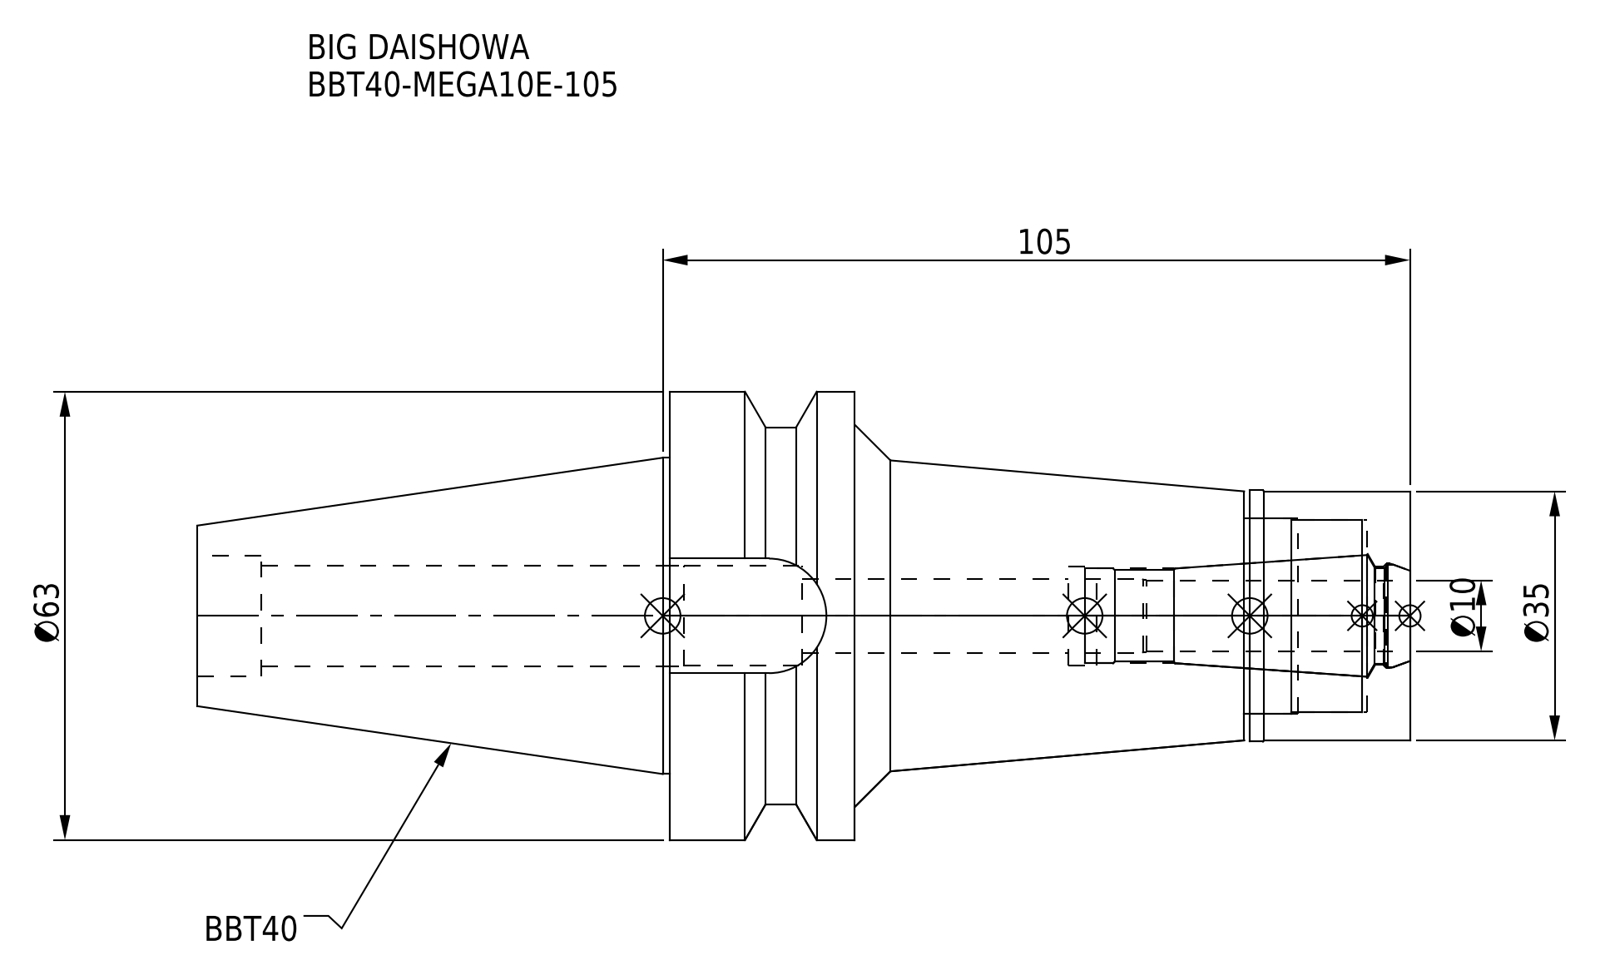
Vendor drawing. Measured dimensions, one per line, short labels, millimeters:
name: DXF_TEMP_ASSY_ASM_4_ASM.stp; BBT40ME10105-100_ASM.stp; MEN10_1.stp; BBT40-MEGA10E-105_1.stp (+3 more)
written by: SolidWorks 2019 (CONFIG_CONTROL_DESIGN)
unit: mm
bodies: 2 solids, 81 faces (21 planar, 40 cylindrical, 20 other)
size: 170.4 × 63 × 63
volume: 202 293 mm³; area: 38 719 mm²
holes: 1× ⌀10.4, 1× ⌀13.3, 1× ⌀13.8, 1× ⌀13.9, 1× ⌀14, 1× ⌀14.2, 1× ⌀14.7, 1× ⌀17, 1× ⌀27, 1× ⌀27.5
bosses: 1× ⌀63, 1× ⌀53, 1× ⌀44.45, 1× ⌀35.3, 1× ⌀35
rounds: 1× R8.05
face distances: 26, 78, 104, 22.5, 55.5, 81.5, 23.3, 0.8, 54.7, 80.7
